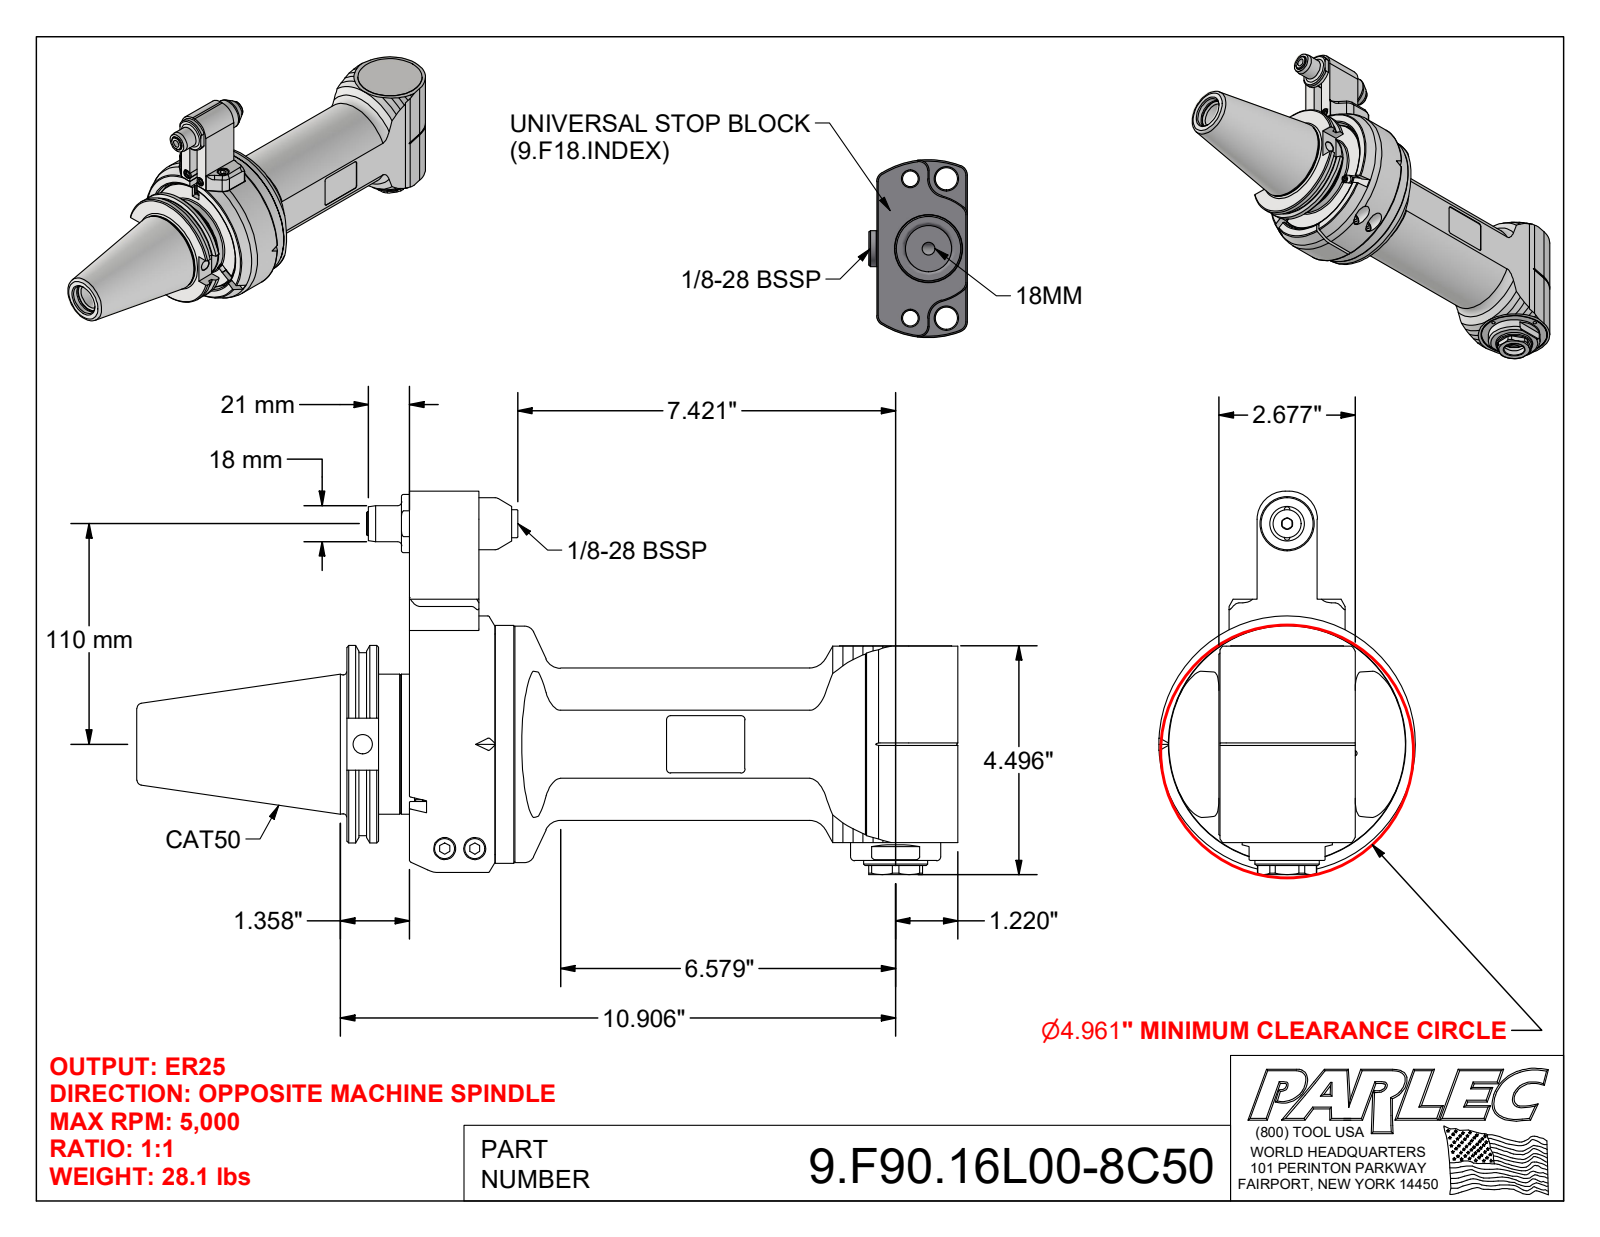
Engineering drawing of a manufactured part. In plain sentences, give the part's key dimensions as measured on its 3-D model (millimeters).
The part is named "9.F90.16L00-8C50; 9GA21C_451 (Type 2, Cat50, 110mm); 9_F90_16L00". Its 3-D file was written by "Autodesk Inventor 2022 (AUTOMOTIVE_DESIGN)". It is 5 solids with 587 faces: 241 planar, 148 cylindrical and 198 other. Overall it measures 409.6 by 191.3 by 128 millimeters. Its volume is 2 178 000 cubic millimeters and its surface area 236 500 square millimeters. Round holes: 20 of diameter 10.5, 4 of diameter 3.2, 4 of diameter 5, 2 of diameter 2.6, 2 of diameter 4.2, 2 of diameter 5.3, 2 of diameter 8, 2 of diameter 10.4, 2 of diameter 11, 2 of diameter 12.5, 1 of diameter 2.5, 1 of diameter 3. Round bosses or shafts: 4 of diameter 10, 4 of diameter 6, 2 of diameter 18, 2 of diameter 2.5, 1 of diameter 128, 1 of diameter 118.6, 1 of diameter 118, 1 of diameter 99. Partial cylindrical surfaces (rounded edges, fillets, slot ends): 12 of radius 2, 4 of radius 4, 2 of radius 0.4, 2 of radius 0.5, 2 of radius 1, 2 of radius 3.5, 2 of radius 8, 2 of radius 14. The main face-to-face distances are 35, 68, 6, 5, 35.5, 8.5, 34, 40, 0.5, 1. The hole center spacings are 66.1, 56.3, 46.8, 92.6, 13, 45.3, 74.7, 25.8.
